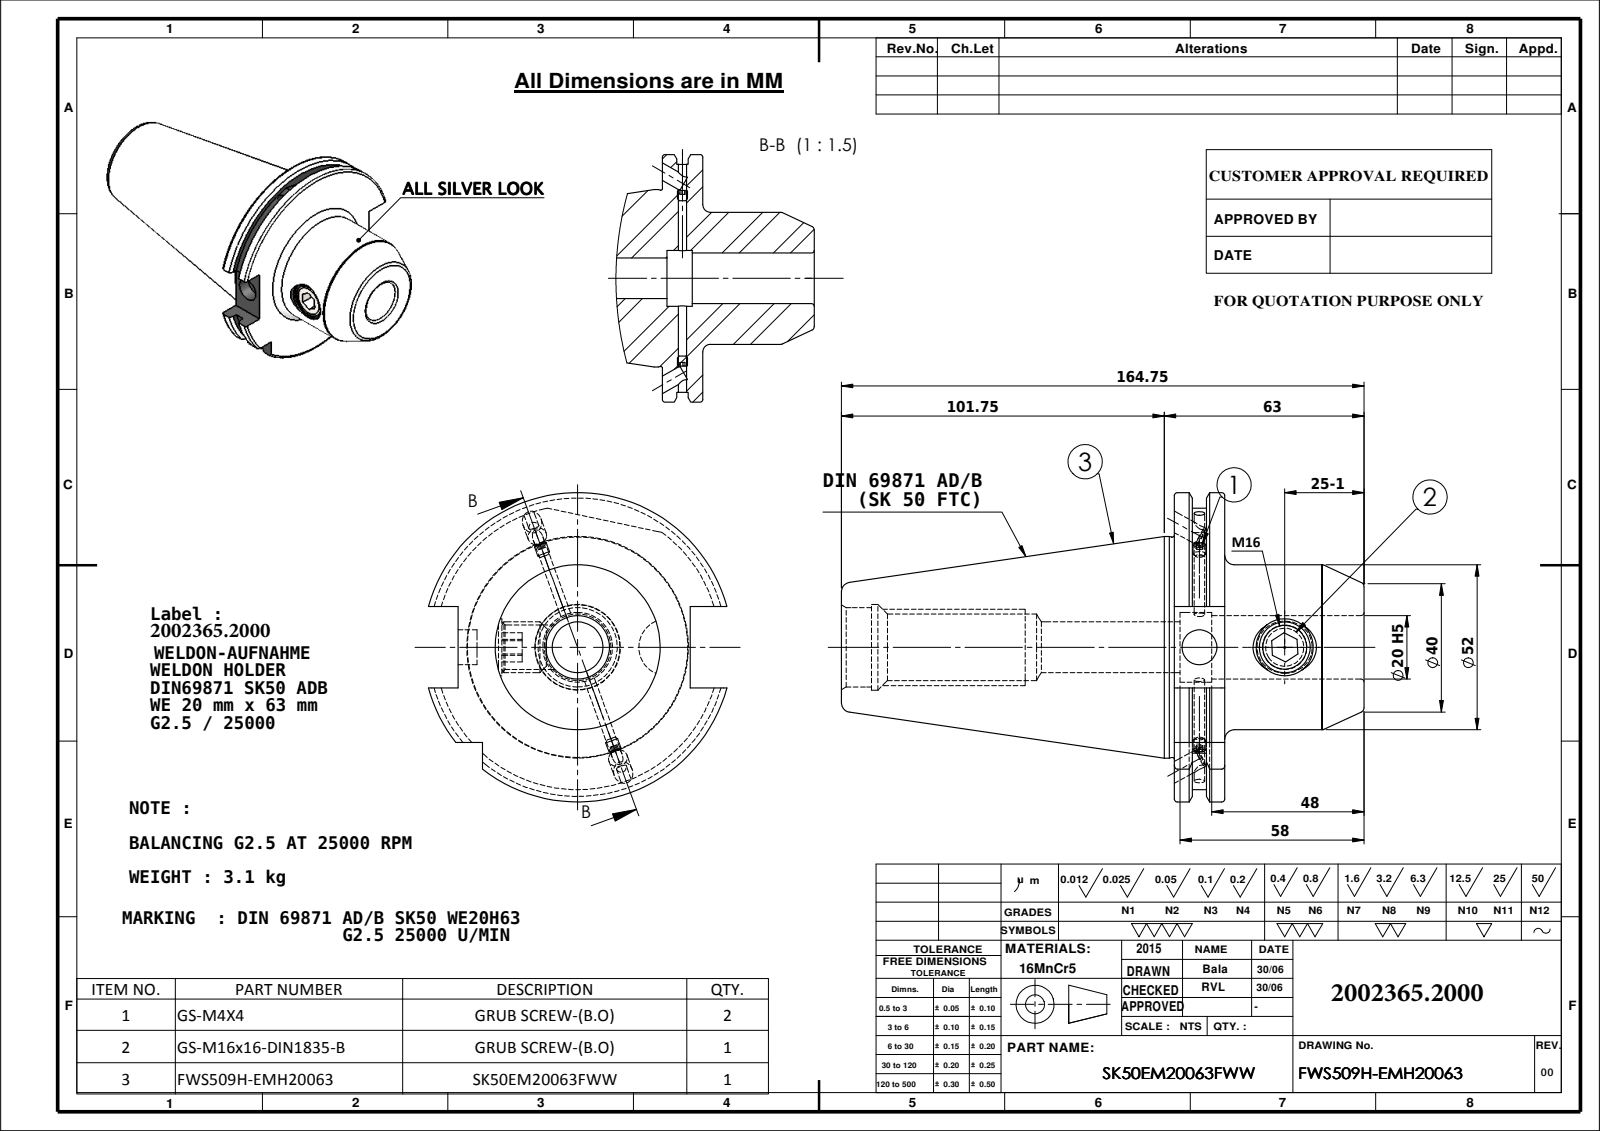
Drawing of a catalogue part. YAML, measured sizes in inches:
part_name: "SK50EM20063FWW; M16X16_ISO 4026 - M16 x 10-N; 91506-WE720063; Copy of M4X4_DIN 913 - M4 x 4-N"
step_written_by: "SolidWorks 2009 (CONFIG_CONTROL_DESIGN)"
units: inches
bodies: {solids: 4, faces: 169, planar: 53, cylindrical: 55, other: 61}
overall_size: [6.486, 3.839, 3.703]
volume: 24.21
surface_area: 85.39
round_holes:
  - {diameter: 0.236, count: 2}
  - {diameter: 0.13, count: 1}
  - {diameter: 0.433, count: 1}
  - {diameter: 0.551, count: 1}
  - {diameter: 0.63, count: 1}
  - {diameter: 0.709, count: 1}
  - {diameter: 0.787, count: 1}
  - {diameter: 0.827, count: 1}
  - {diameter: 0.866, count: 1}
  - {diameter: 0.984, count: 1}
  - {diameter: 1.063, count: 1}
round_bosses_or_shafts:
  - {diameter: 0.157, count: 2}
  - {diameter: 2.75, count: 1}
  - {diameter: 2.734, count: 1}
  - {diameter: 2.047, count: 1}
  - {diameter: 0.63, count: 1}
partial_cylinders:
  - {radius: 1.768, count: 1}
  - {radius: 1.919, count: 1}
face_to_face_distances: [0.626, 2.354, 1.728, 0.223, 0.403, 2.131, 0.4, 0.177, 0.226, 1.955]
hole_center_spacings: [1.059]
